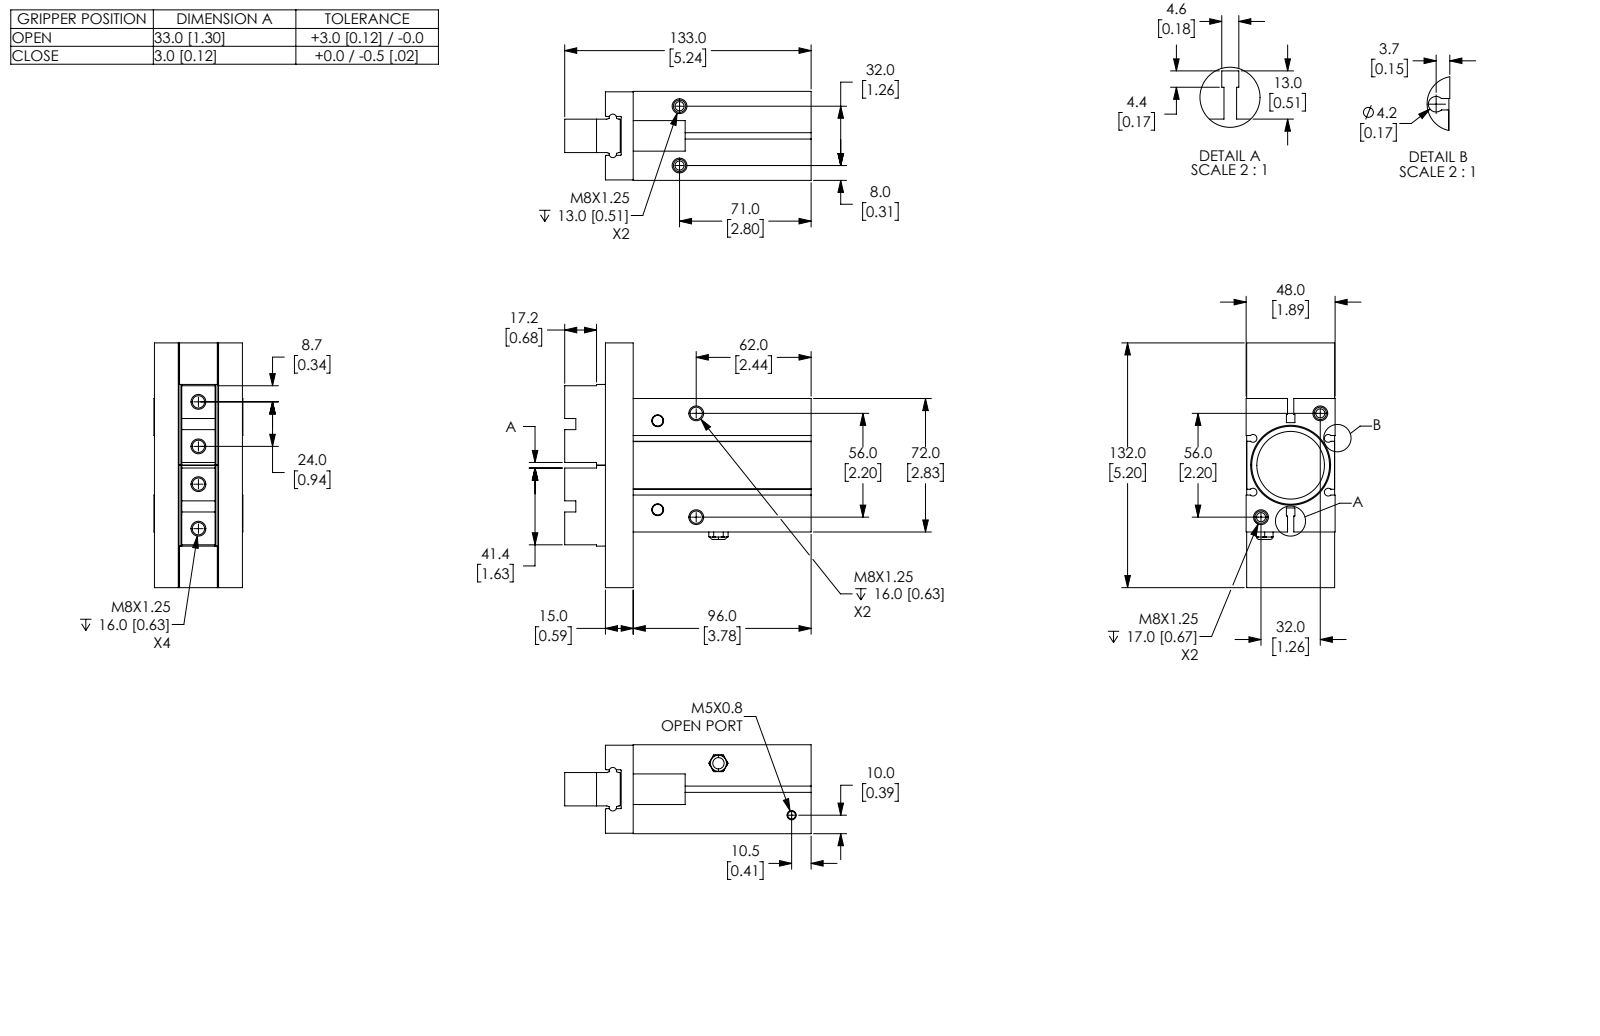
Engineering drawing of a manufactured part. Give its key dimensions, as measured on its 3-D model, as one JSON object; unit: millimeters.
{"part_name": "KP40MSC-MB; KP40MSC-MB-3; KP40MSC-MB-2; KP40MSC-MB-1", "step_written_by": "SolidWorks 2017 (CONFIG_CONTROL_DESIGN)", "units": "millimeters", "bodies": {"solids": 3, "faces": 262, "planar": 135, "cylindrical": 65, "other": 62}, "overall_size": [133, 132, 48], "volume_mm3": 384779, "surface_area_mm2": 72715, "round_holes": [[6.65, 8], [0.5, 2], [4.13, 2], [6.65, 2], [8.02, 2], [6.1, 1], [36.5, 1], [42, 1]], "partial_cylinders_radius": [[0.2, 7], [2.1, 4], [0.3, 2], [2, 2]], "face_to_face_distances": [15, 47.7, 15.75, 32.25, 15.45, 31.95, 47.75, 15.5, 32, 47.45], "hole_center_spacings": [10.2, 17.16, 23.93, 24, 32.25, 34.2, 41.42, 44.4]}
